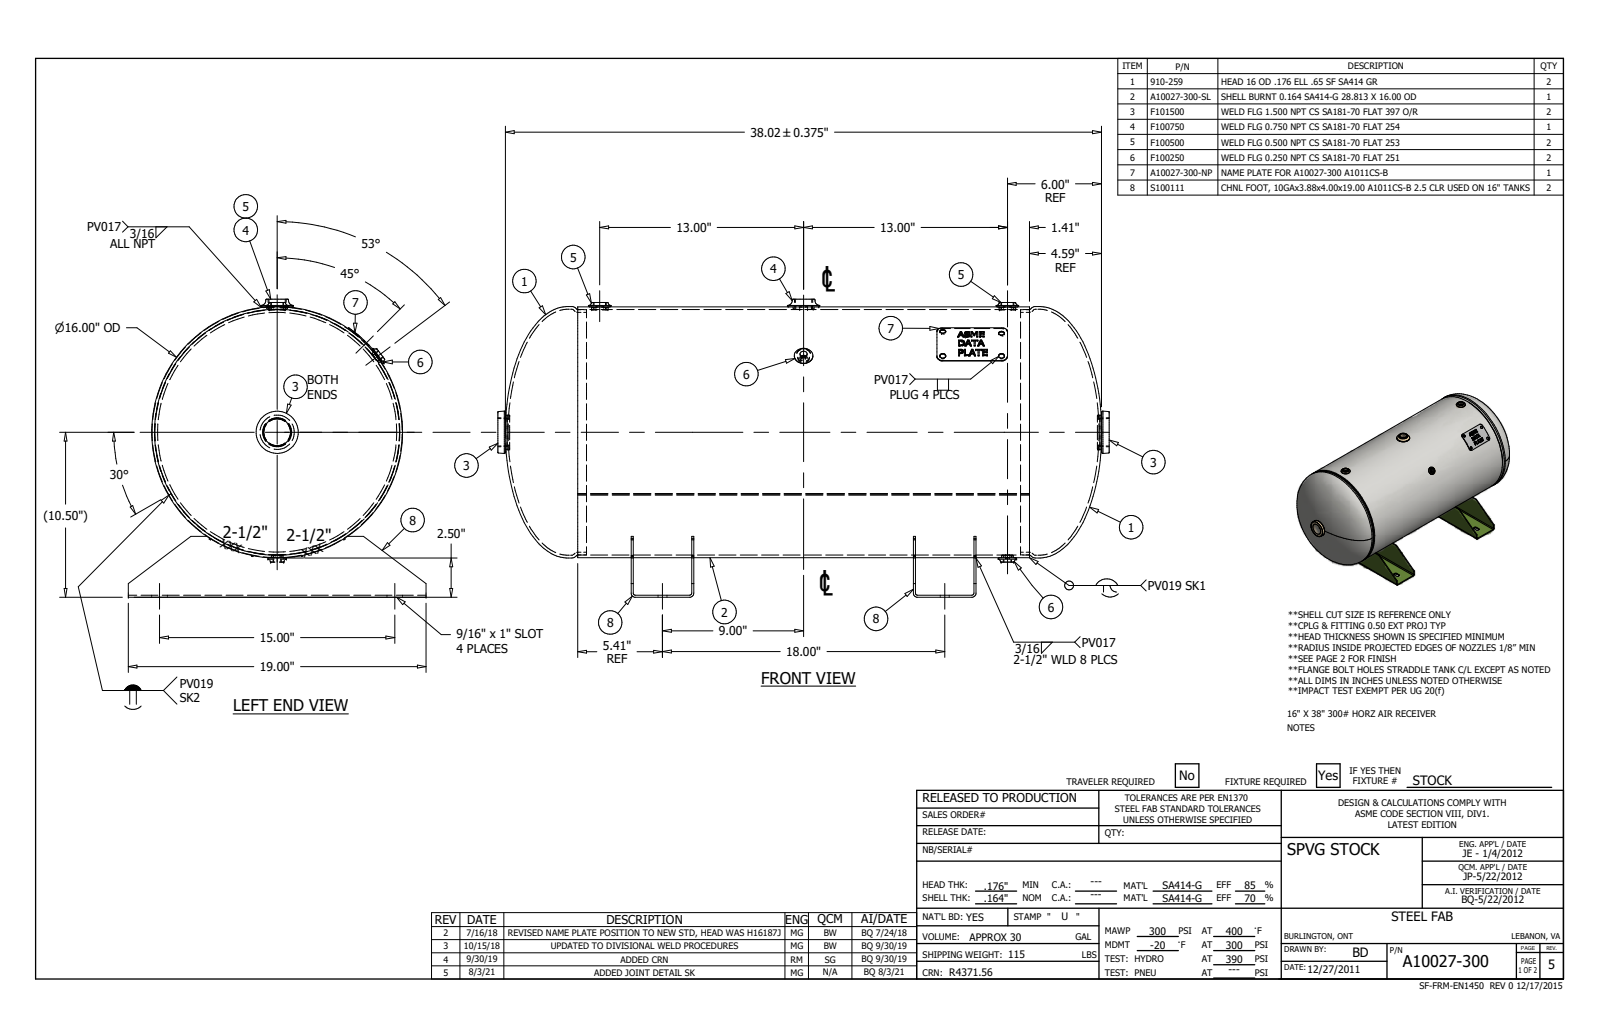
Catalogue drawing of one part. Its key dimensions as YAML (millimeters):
part_name: "A10027-300; A10027-300SL; 910-259; F100750 (+5 more)"
step_written_by: "Autodesk Inventor 2017 (AUTOMOTIVE_DESIGN)"
units: millimeters
bodies: {solids: 19, faces: 410, planar: 225, cylindrical: 101, other: 84}
overall_size: [990.41, 482.6, 481.91]
volume: 6569000
surface_area: 3236000
round_holes:
  - {diameter: 9.52, count: 4}
  - {diameter: 12.7, count: 3}
  - {diameter: 6.35, count: 2}
  - {diameter: 11.46, count: 2}
  - {diameter: 18.64, count: 2}
  - {diameter: 43.26, count: 1}
  - {diameter: 387.3, count: 1}
  - {diameter: 396.68, count: 1}
  - {diameter: 397.46, count: 1}
  - {diameter: 406.4, count: 1}
round_bosses_or_shafts:
  - {diameter: 26.99, count: 2}
  - {diameter: 405.02, count: 1}
  - {diameter: 396.24, count: 1}
  - {diameter: 55.56, count: 1}
  - {diameter: 52.39, count: 1}
  - {diameter: 36.91, count: 1}
partial_cylinders:
  - {radius: 7.14, count: 8}
  - {radius: 3.42, count: 4}
  - {radius: 6.83, count: 4}
  - {radius: 9.53, count: 4}
  - {radius: 204.72, count: 1}
  - {radius: 204.73, count: 1}
face_to_face_distances: [3.42, 457.2, 98.18, 460.62, 453.78, 94.76, 555.38, 359.02, 101.6, 551.96]
hole_center_spacings: [330.2, 0.62, 51.09, 55.85, 95.25, 95.37, 108.09, 110.42]
